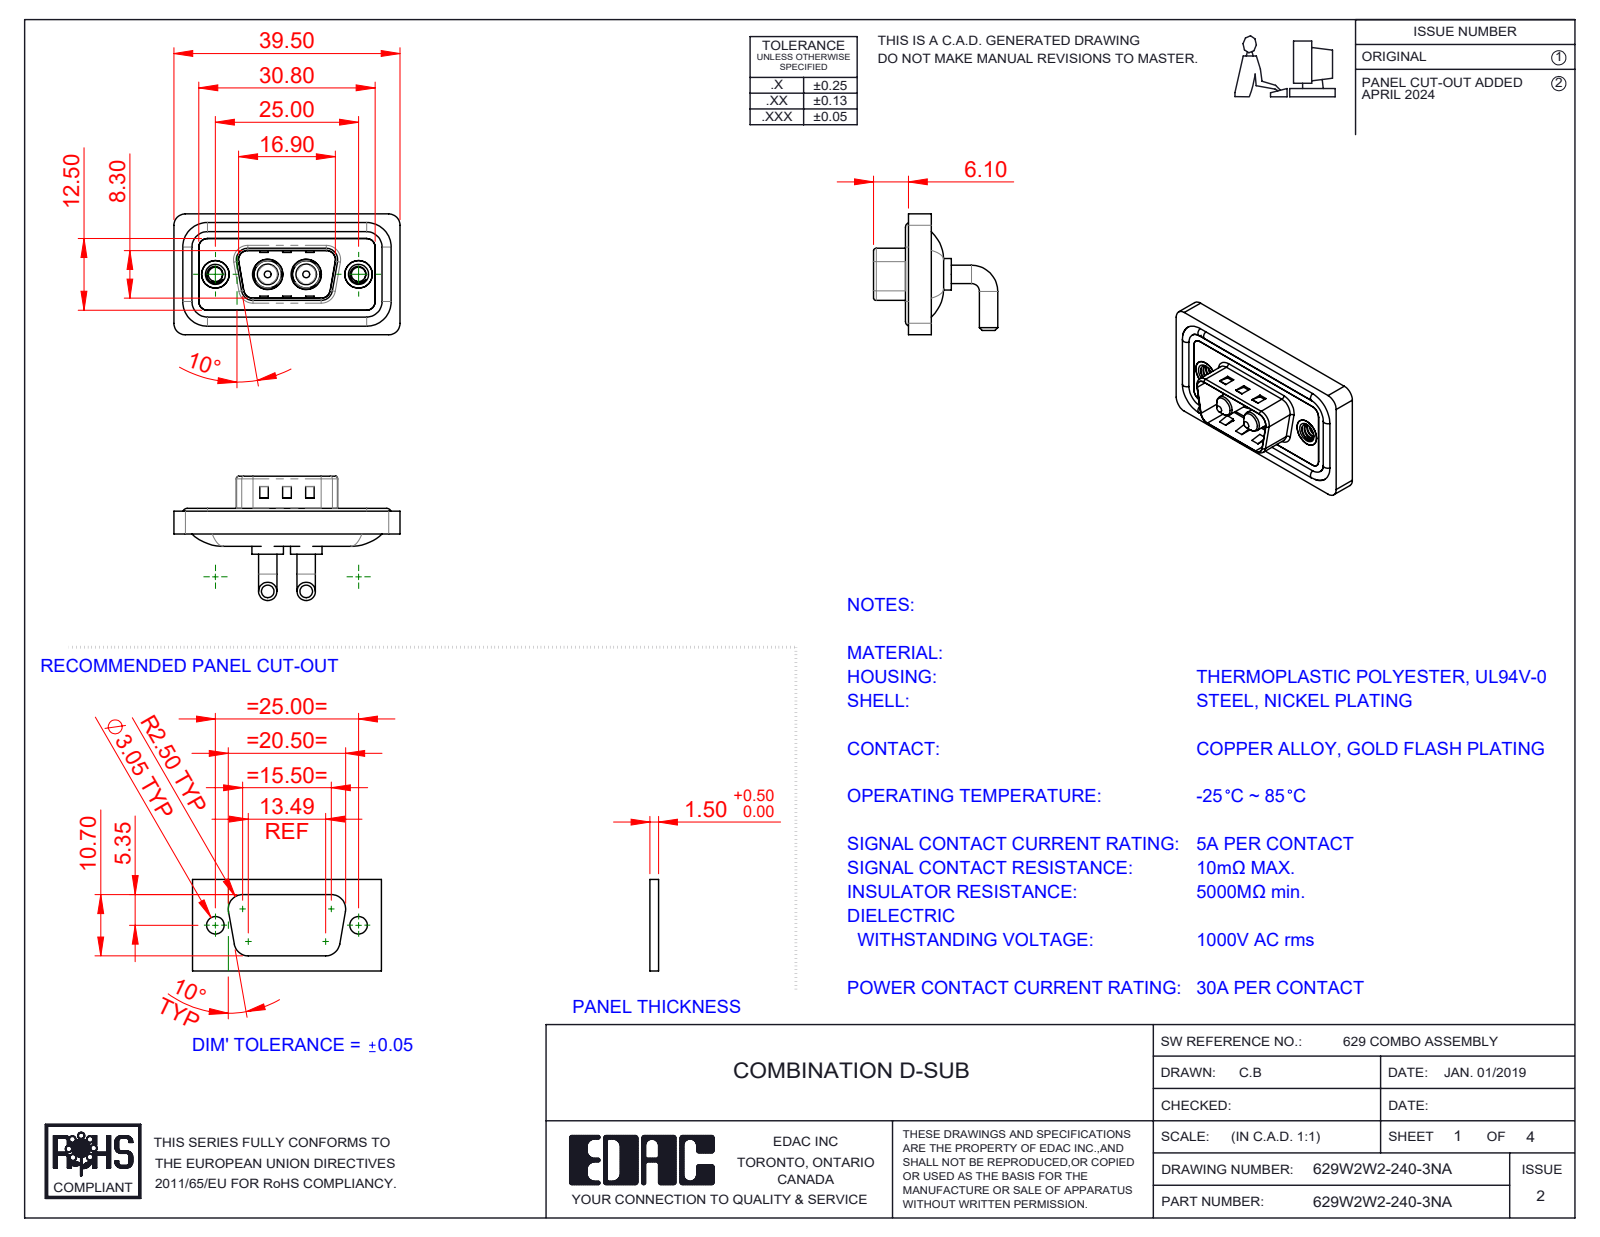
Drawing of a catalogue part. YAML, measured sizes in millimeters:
part_name: "629Combo Threaded Rivet_A; 629Combo Housing_2W2; 629Combo Waterproof Housing_09 Contacts; 629Combo Shell Rear_09 Contacts (+3 more)"
step_written_by: "SolidWorks 2023 (CONFIG_CONTROL_DESIGN)"
units: millimeters
bodies: {solids: 11, faces: 491, planar: 165, cylindrical: 220, other: 106}
overall_size: [39.5, 21.7, 21.1]
volume: 4644
surface_area: 7208
round_holes:
  - {diameter: 2.5, count: 2}
  - {diameter: 4, count: 2}
  - {diameter: 4.8, count: 2}
  - {diameter: 4.85, count: 2}
  - {diameter: 5, count: 2}
  - {diameter: 5.3, count: 2}
round_bosses_or_shafts:
  - {diameter: 3.2, count: 4}
  - {diameter: 1.6, count: 4}
  - {diameter: 5.5, count: 2}
  - {diameter: 5.2, count: 2}
  - {diameter: 4.9, count: 2}
  - {diameter: 4.75, count: 2}
  - {diameter: 3.75, count: 2}
  - {diameter: 3.6, count: 2}
partial_cylinders:
  - {radius: 1.5, count: 18}
  - {radius: 2, count: 18}
  - {radius: 0.5, count: 8}
  - {radius: 1.6, count: 8}
  - {radius: 0.25, count: 4}
  - {radius: 0.6, count: 4}
  - {radius: 0.65, count: 4}
  - {radius: 0.9, count: 4}
face_to_face_distances: [0.4, 2.9, 1.1, 0.8, 2.1, 2.5, 3.1, 1.6, 4.5, 1.5]
hole_center_spacings: [9.14, 15.86, 6.72, 25]
